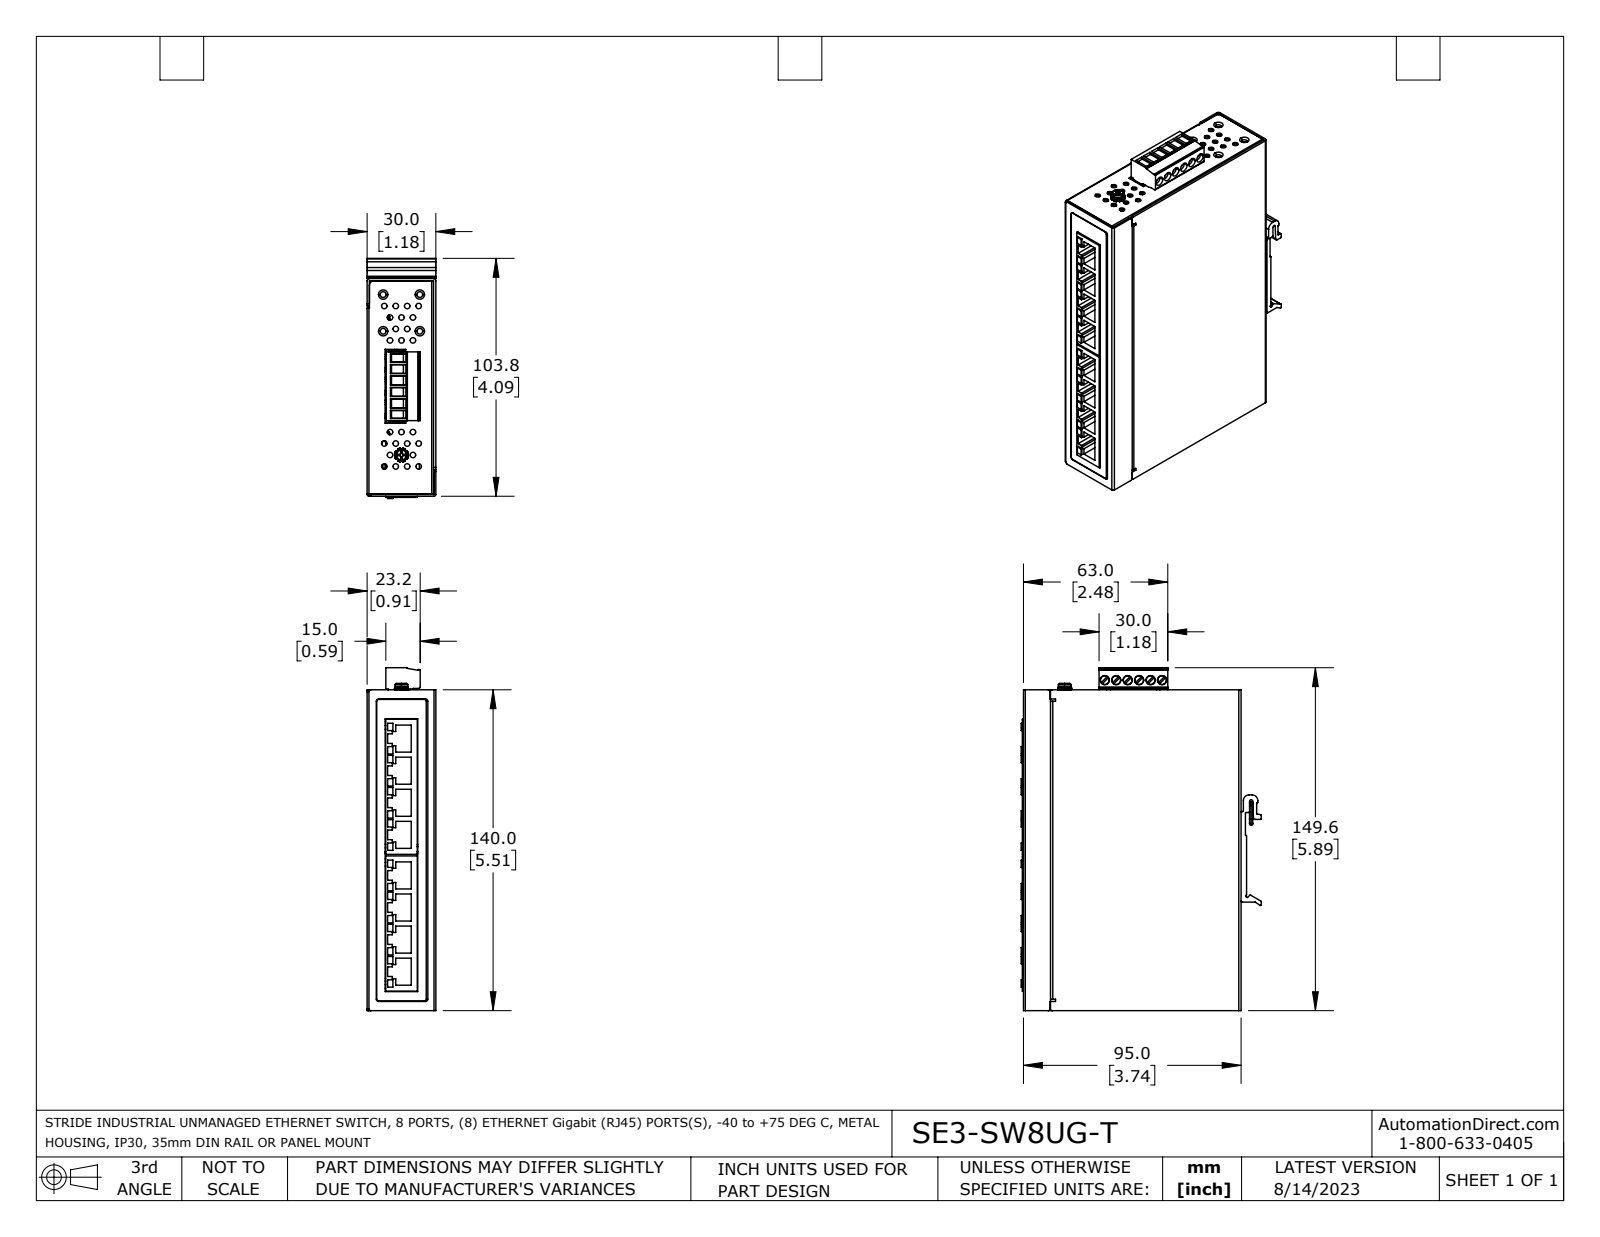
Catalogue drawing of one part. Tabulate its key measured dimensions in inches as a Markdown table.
| quantity | value |
| --- | --- |
| part name | LEONTON_EG2-0800_3D sr1 solid but 16 bad faces1 extTB1ac coord fxt sr1 |
| STEP written by | SolidWorks 2021 (AUTOMOTIVE_DESIGN) |
| units | inches |
| bodies | 29 solids, 2121 faces (1049 planar, 701 cylindrical, 371 other) |
| overall size | 5.891 × 4.126 × 1.181 |
| volume | 4.665 in³ |
| surface area | 174 in² |
| round holes (diameter × count) | 0.094 × 51, 0.098 × 14, 0.157 × 9, 0.217 × 4, 0.138 × 2, 0.059 × 1 |
| round bosses / shafts (diameter × count) | 0.161 × 10, 0.118 × 7, 0.149 × 6, 0.055 × 6, 0.035 × 6, 0.197 × 5, 0.094 × 5, 0.248 × 4 |
| partial cylindrical surfaces (radius × count) | 0.004 × 47, 0.031 × 30, 0.01 × 24, 0.039 × 19, 0.012 × 14, 0.008 × 13, 0.02 × 9, 0.079 × 9 |
| main face-to-face distances | 0.039, 0.031, 1.142, 1.11, 1.181, 1.15, 0.319, 0.862, 0.823, 0.28 |
| hole center spacings | 0.22, 0.394, 0.197, 0.44, 2.168, 0.355, 0.599, 1.774 |
